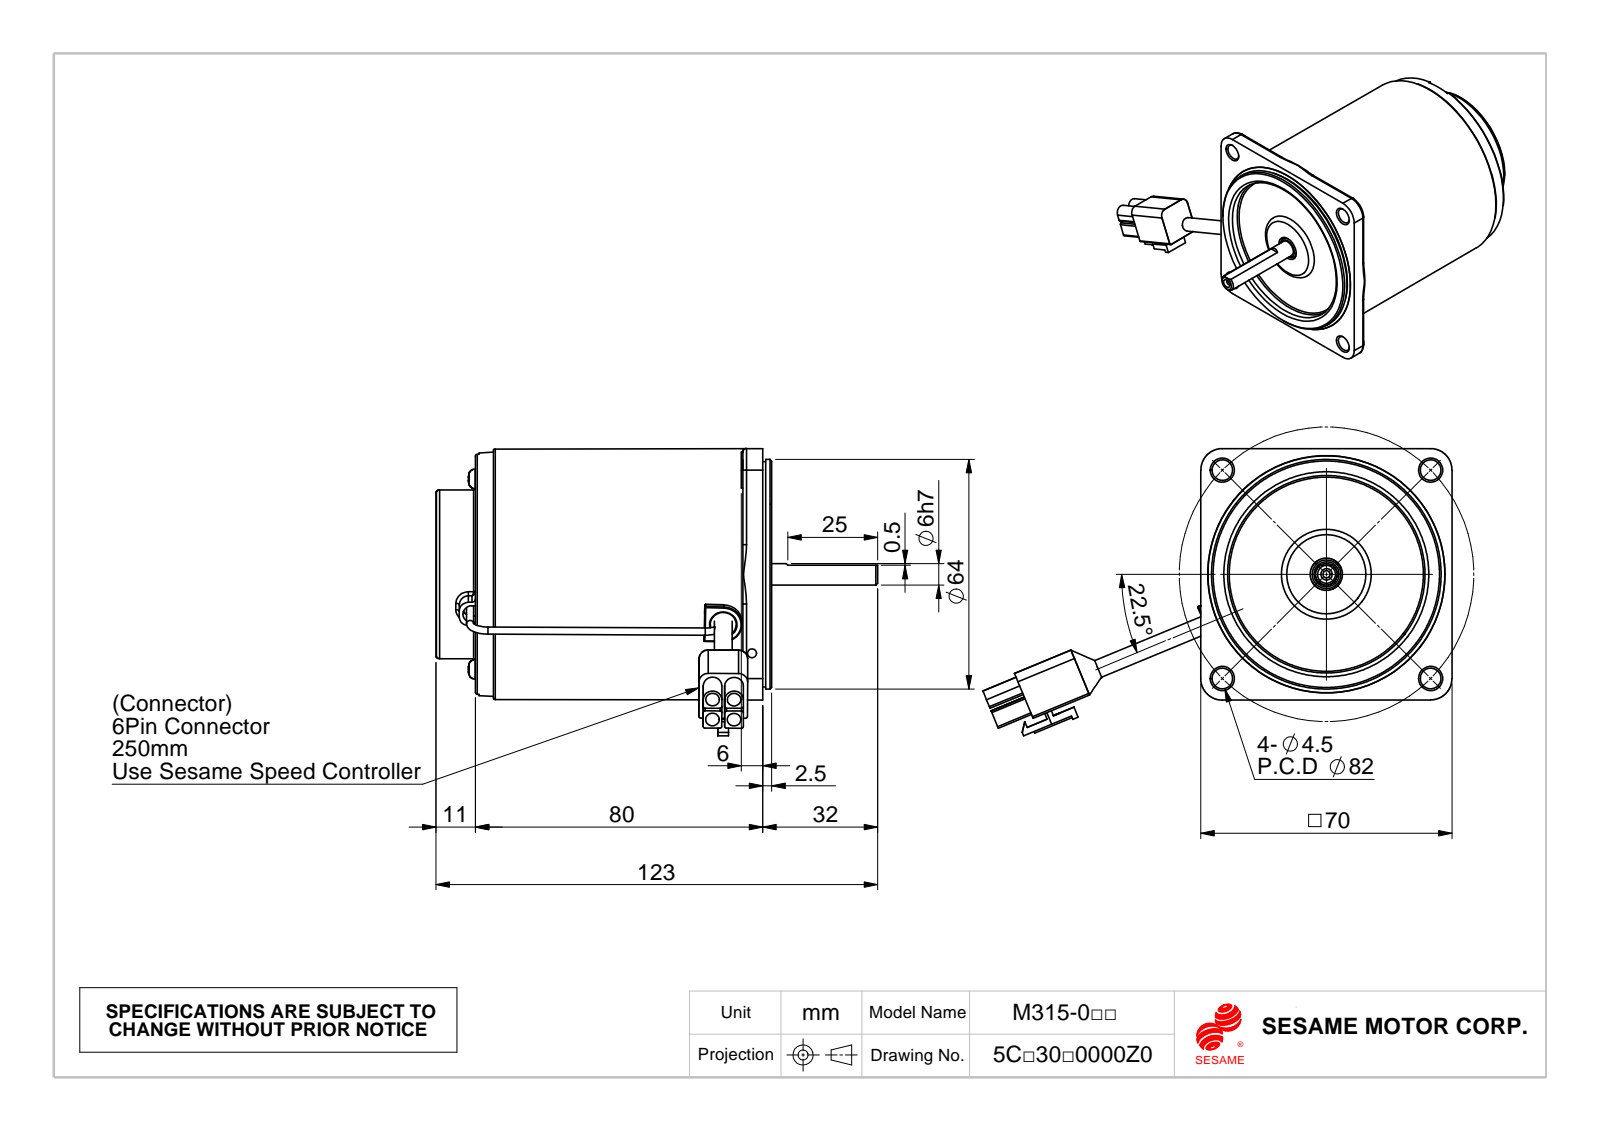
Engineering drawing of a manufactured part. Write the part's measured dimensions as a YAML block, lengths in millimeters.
part_name: "公端子; M315-RK-R-模型_3.鑽孔; 線扣; C364_車工(成品) (+1 more)"
step_written_by: "SolidWorks 2010 (CONFIG_CONTROL_DESIGN)"
units: millimeters
bodies: {solids: 9, faces: 468, planar: 175, cylindrical: 177, other: 116}
overall_size: [130.68, 123, 79.96]
volume: 337487
surface_area: 51761
round_holes:
  - {diameter: 2.5, count: 5}
  - {diameter: 3.8, count: 4}
  - {diameter: 4.2, count: 4}
  - {diameter: 5.5, count: 4}
  - {diameter: 5.75, count: 4}
  - {diameter: 2, count: 2}
  - {diameter: 3.1, count: 2}
  - {diameter: 7.2, count: 1}
  - {diameter: 9, count: 1}
  - {diameter: 9.5, count: 1}
  - {diameter: 15, count: 1}
  - {diameter: 18, count: 1}
round_bosses_or_shafts:
  - {diameter: 10, count: 4}
  - {diameter: 5.5, count: 2}
  - {diameter: 3, count: 2}
  - {diameter: 2, count: 2}
  - {diameter: 63.93, count: 1}
  - {diameter: 62.73, count: 1}
  - {diameter: 58, count: 1}
  - {diameter: 57.42, count: 1}
partial_cylinders:
  - {radius: 0.5, count: 14}
  - {radius: 1, count: 10}
  - {radius: 0.25, count: 8}
  - {radius: 0.3, count: 8}
  - {radius: 2.5, count: 7}
  - {radius: 6, count: 4}
  - {radius: 2.6, count: 2}
  - {radius: 5.25, count: 1}
face_to_face_distances: [77.4, 77.5, 1.51, 75.89, 1.61, 1.5, 1.6, 79, 3.11, 12]
hole_center_spacings: [43.34, 6, 14, 4.24, 10.72, 19.33, 19.8, 25.87]
